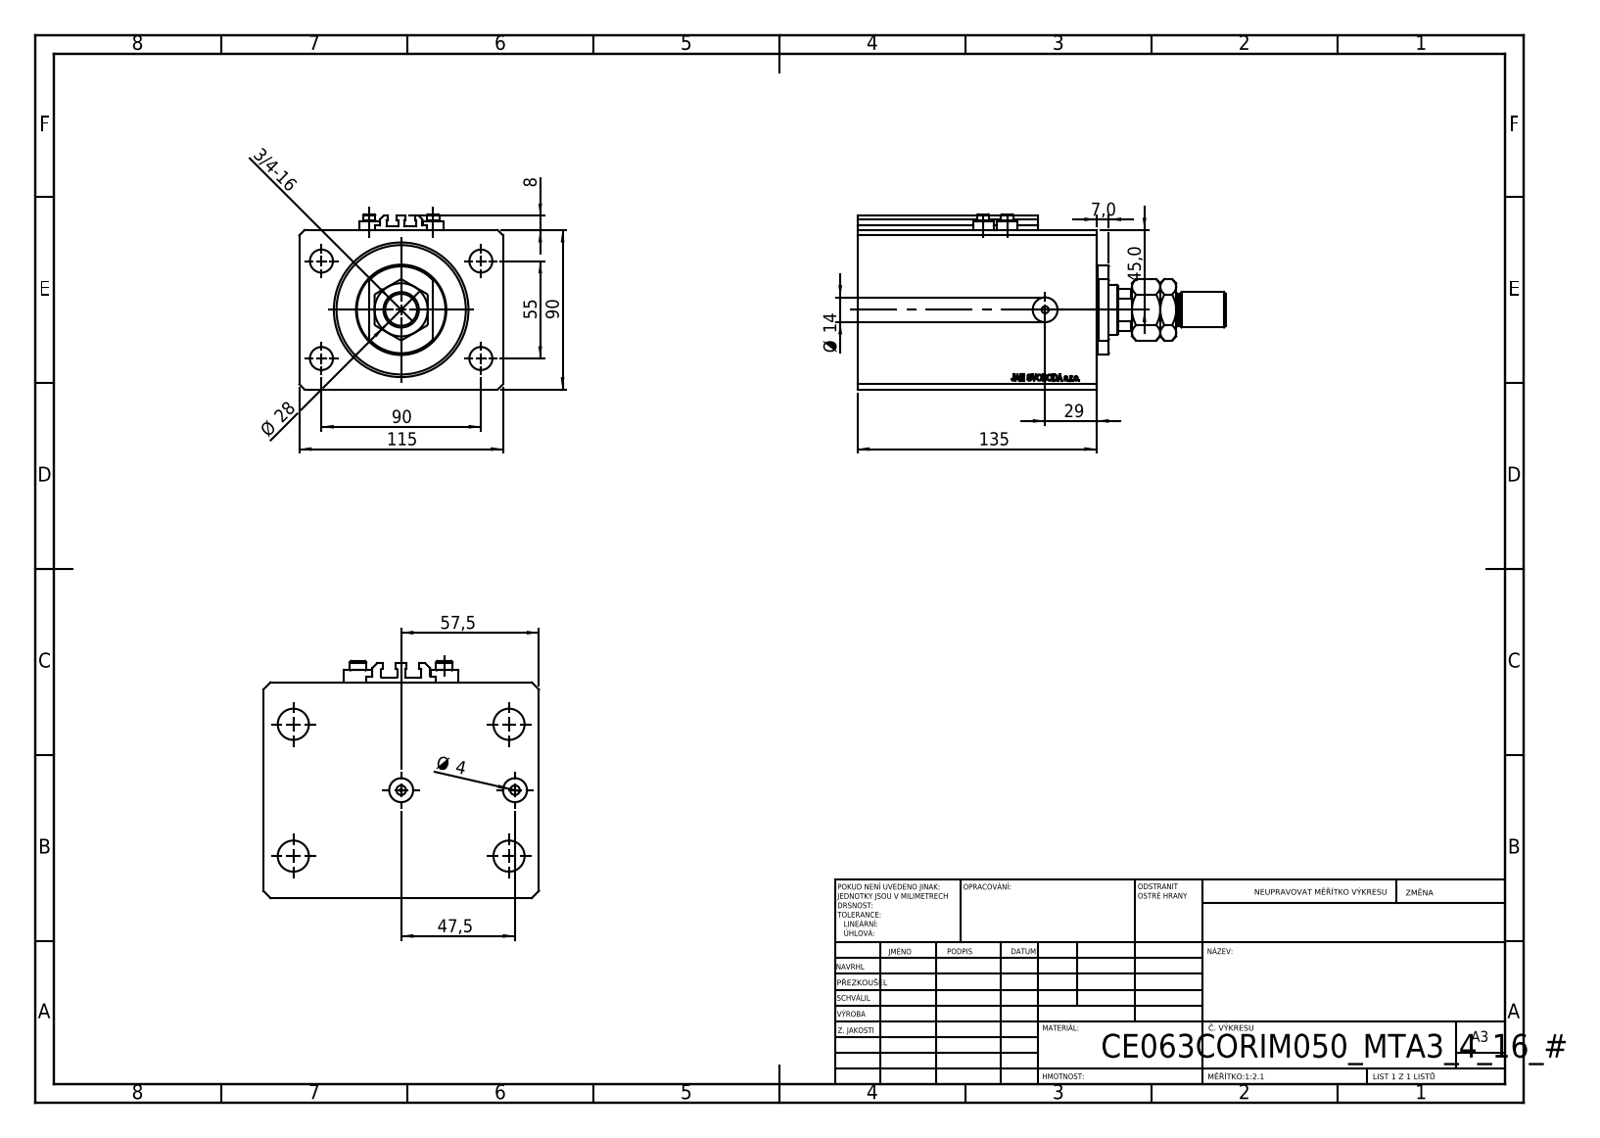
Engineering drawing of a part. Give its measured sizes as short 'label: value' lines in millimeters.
name: V250CE_C_Body; V250CE_C_VCP; V250CE_VC_C; MTA (+1 more)
written by: SolidWorks 2019 (CONFIG_CONTROL_DESIGN)
unit: mm
bodies: 9 solids, 1087 faces (519 planar, 92 cylindrical, 476 other)
size: 208 × 115 × 99
volume: 1 247 000 mm³; area: 182 630 mm²
holes: 8× ⌀4, 4× ⌀13, 2× ⌀10, 2× ⌀14, 1× ⌀1.25, 1× ⌀18.5, 1× ⌀28, 1× ⌀63, 1× ⌀76
bosses: 4× ⌀11.6, 4× ⌀7, 1× ⌀50, 1× ⌀20, 1× ⌀18
rounds: 10× R0.2, 1× R13.5
face distances: 115, 90, 135, 20, 17.9, 117.1, 97.1, 65, 50, 47.1
hole spacings: 52.74, 13.6, 27.61, 36, 38.48, 55, 90, 96.5
